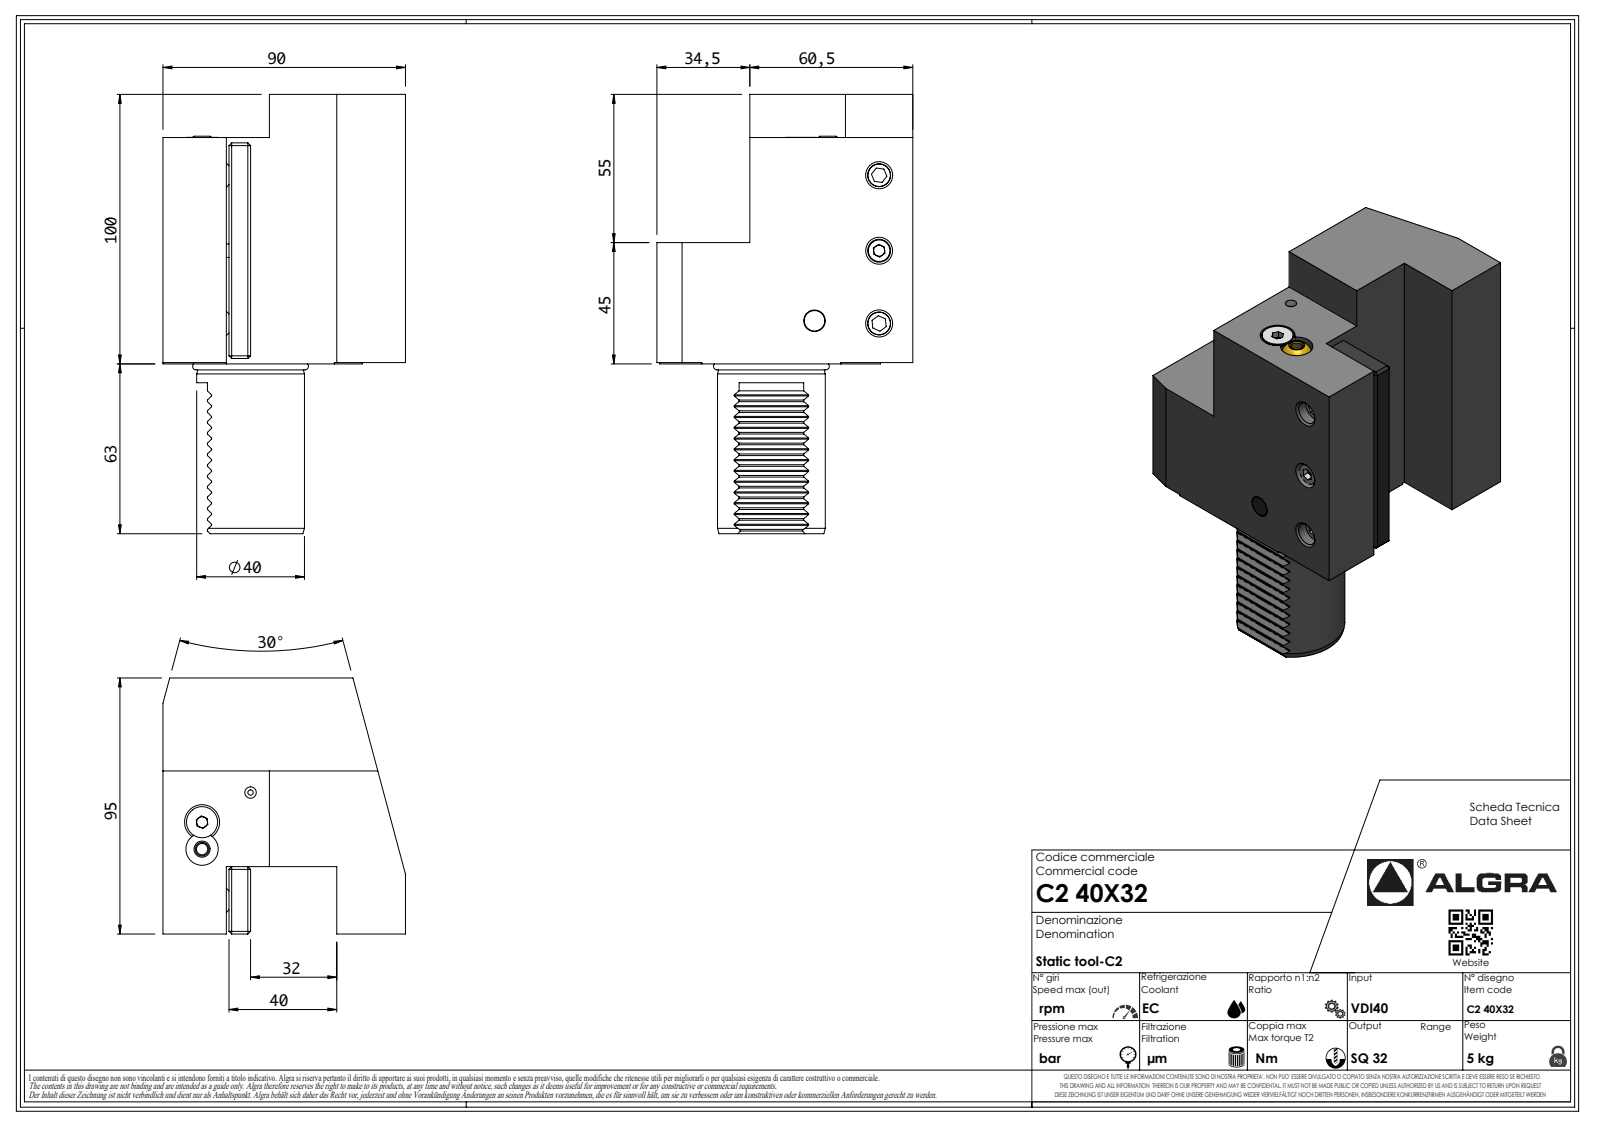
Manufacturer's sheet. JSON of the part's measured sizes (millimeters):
{"part_name": "C240X32", "step_written_by": "SolidWorks 2023 (AUTOMOTIVE_DESIGN)", "units": "millimeters", "bodies": {"solids": 1, "faces": 325, "planar": 225, "cylindrical": 44, "other": 56}, "overall_size": [163, 95, 90], "volume_mm3": 595648, "surface_area_mm2": 60990, "round_holes": [[2.1, 1]], "round_bosses_or_shafts": [[40, 1], [38.7, 1], [6.37, 1], [5, 1], [1.7, 1]], "partial_cylinders_radius": [[0.3, 13], [0.33, 7], [0.52, 7], [3.7, 7], [0.21, 1], [41.5, 1]], "face_to_face_distances": [25, 60.5, 35.5, 34.5, 95, 70, 16, 45, 64.5, 100]}
